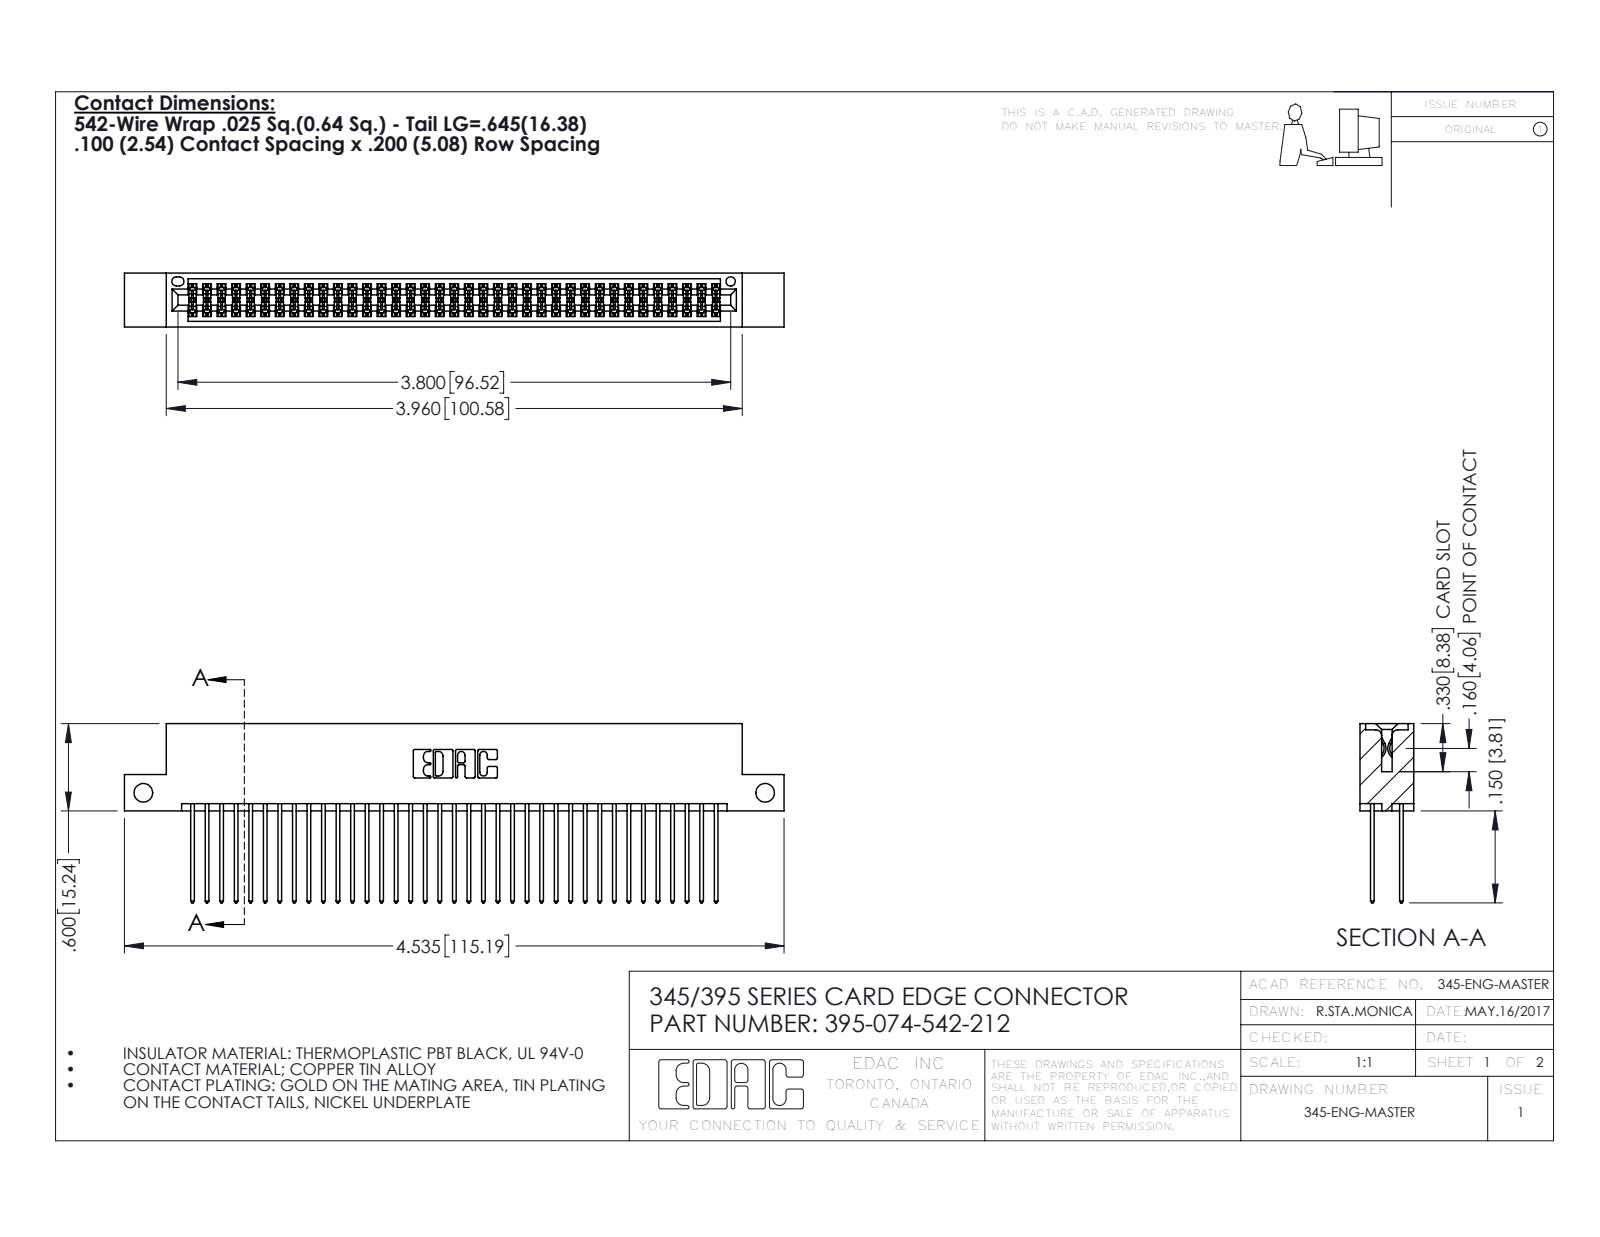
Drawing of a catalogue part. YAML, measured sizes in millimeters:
part_name: "345 Part_Flush Mounting Lugs - Side Mount; 395-074-542-212; 345-292-001_345-293-142"
step_written_by: "SolidWorks 2016 (CONFIG_CONTROL_DESIGN)"
units: millimeters
bodies: {solids: 75, faces: 3826, planar: 2522, cylindrical: 1304, other: 0}
overall_size: [115.2, 31.3, 9.4]
volume: 11400
surface_area: 18230
round_holes:
  - {diameter: 3.3, count: 2}
  - {diameter: 1.6, count: 1}
partial_cylinders:
  - {radius: 0.2, count: 111}
  - {radius: 0.3, count: 74}
  - {radius: 0.3, count: 22}
  - {radius: 0.2, count: 6}
  - {radius: 0.8, count: 6}
  - {radius: 0.7, count: 3}
  - {radius: 0.4, count: 2}
  - {radius: 0.5, count: 2}
face_to_face_distances: [7.6, 1.8, 5.1, 2.5, 6.9, 0.6, 5.7, 9.4, 4.4, 3.8]
hole_center_spacings: [108.6]
